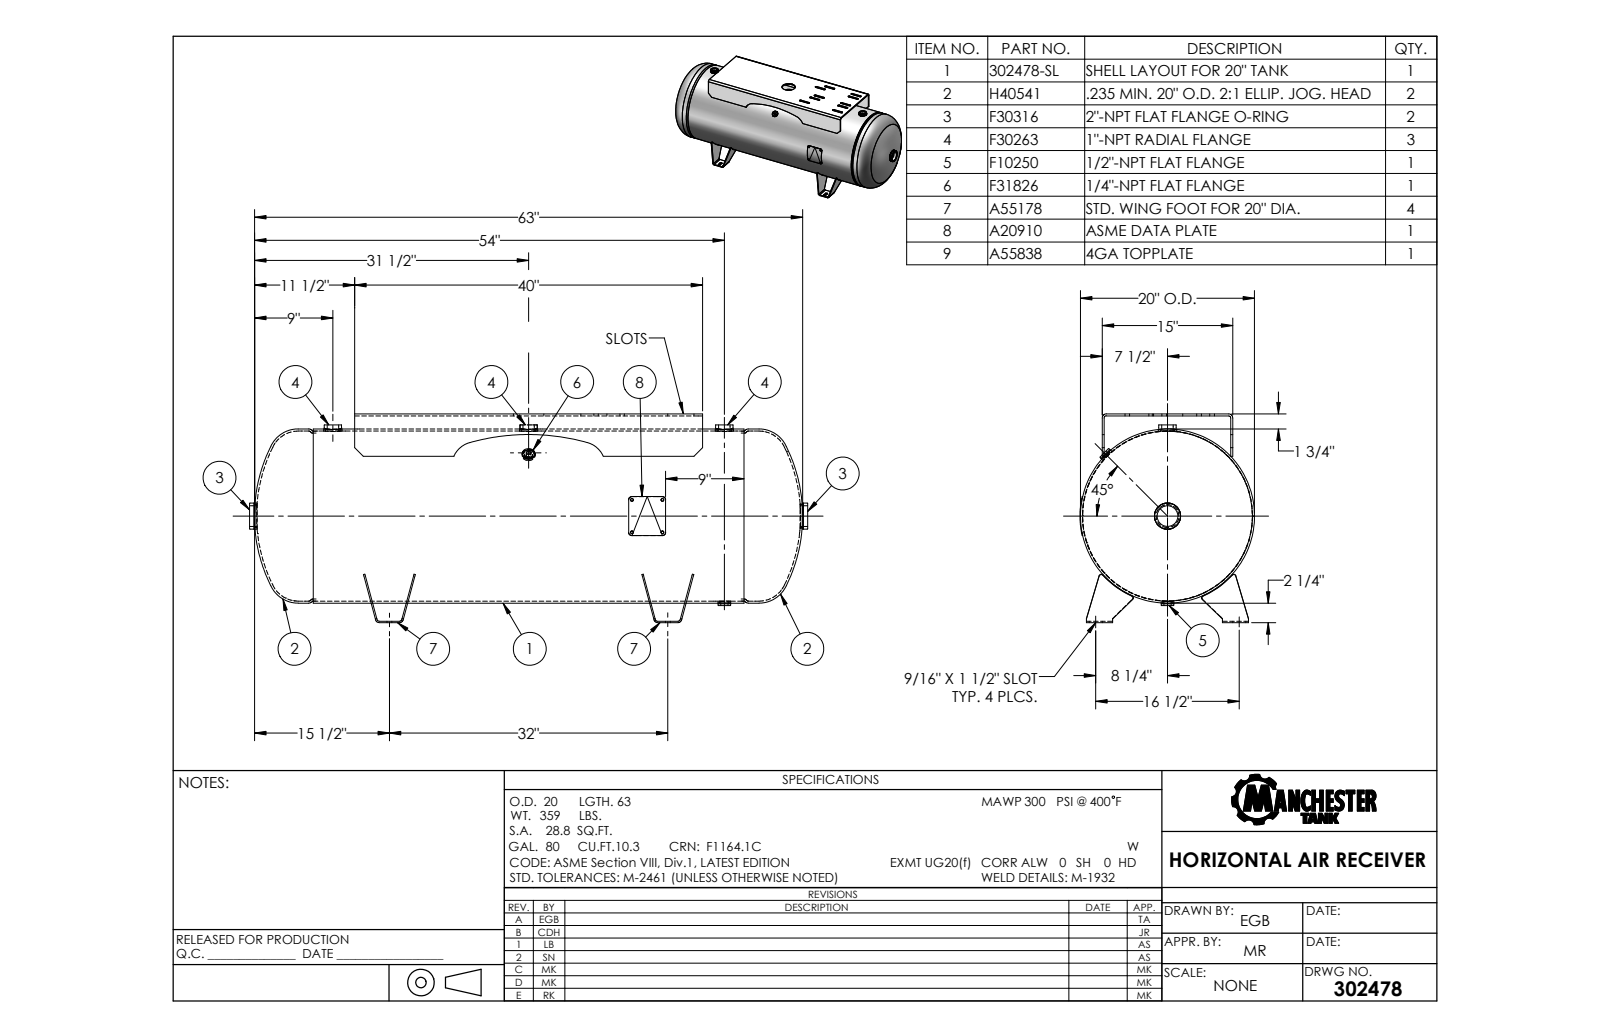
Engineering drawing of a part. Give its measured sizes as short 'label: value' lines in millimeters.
name: 302478
written by: SolidWorks 2011 (CONFIG_CONTROL_DESIGN)
unit: mm
bodies: 0 solids, 367 faces (148 planar, 139 cylindrical, 80 other)
size: 1629.6 × 609.2 × 509.5
holes: 2× ⌀33.4, 1× ⌀13.7, 1× ⌀21.3, 1× ⌀25.4, 1× ⌀33.4, 1× ⌀60.3, 1× ⌀76.3, 1× ⌀88.9, 1× ⌀482.6, 1× ⌀496.5
bosses: 2× ⌀60.3, 1× ⌀508, 1× ⌀495.3, 1× ⌀76.2, 1× ⌀66.7, 1× ⌀46.1, 1× ⌀38.1
rounds: 20× R6.4, 20× R6.8, 8× R7.1, 6× R257.2, 4× R10.5, 2× R7.6, 1× R255.5
face distances: 5.7, 375.3, 4.2, 381, 369.6, 785.2, 789.4, 781, 4.2, 785.1
hole spacings: 571.5, 1143
